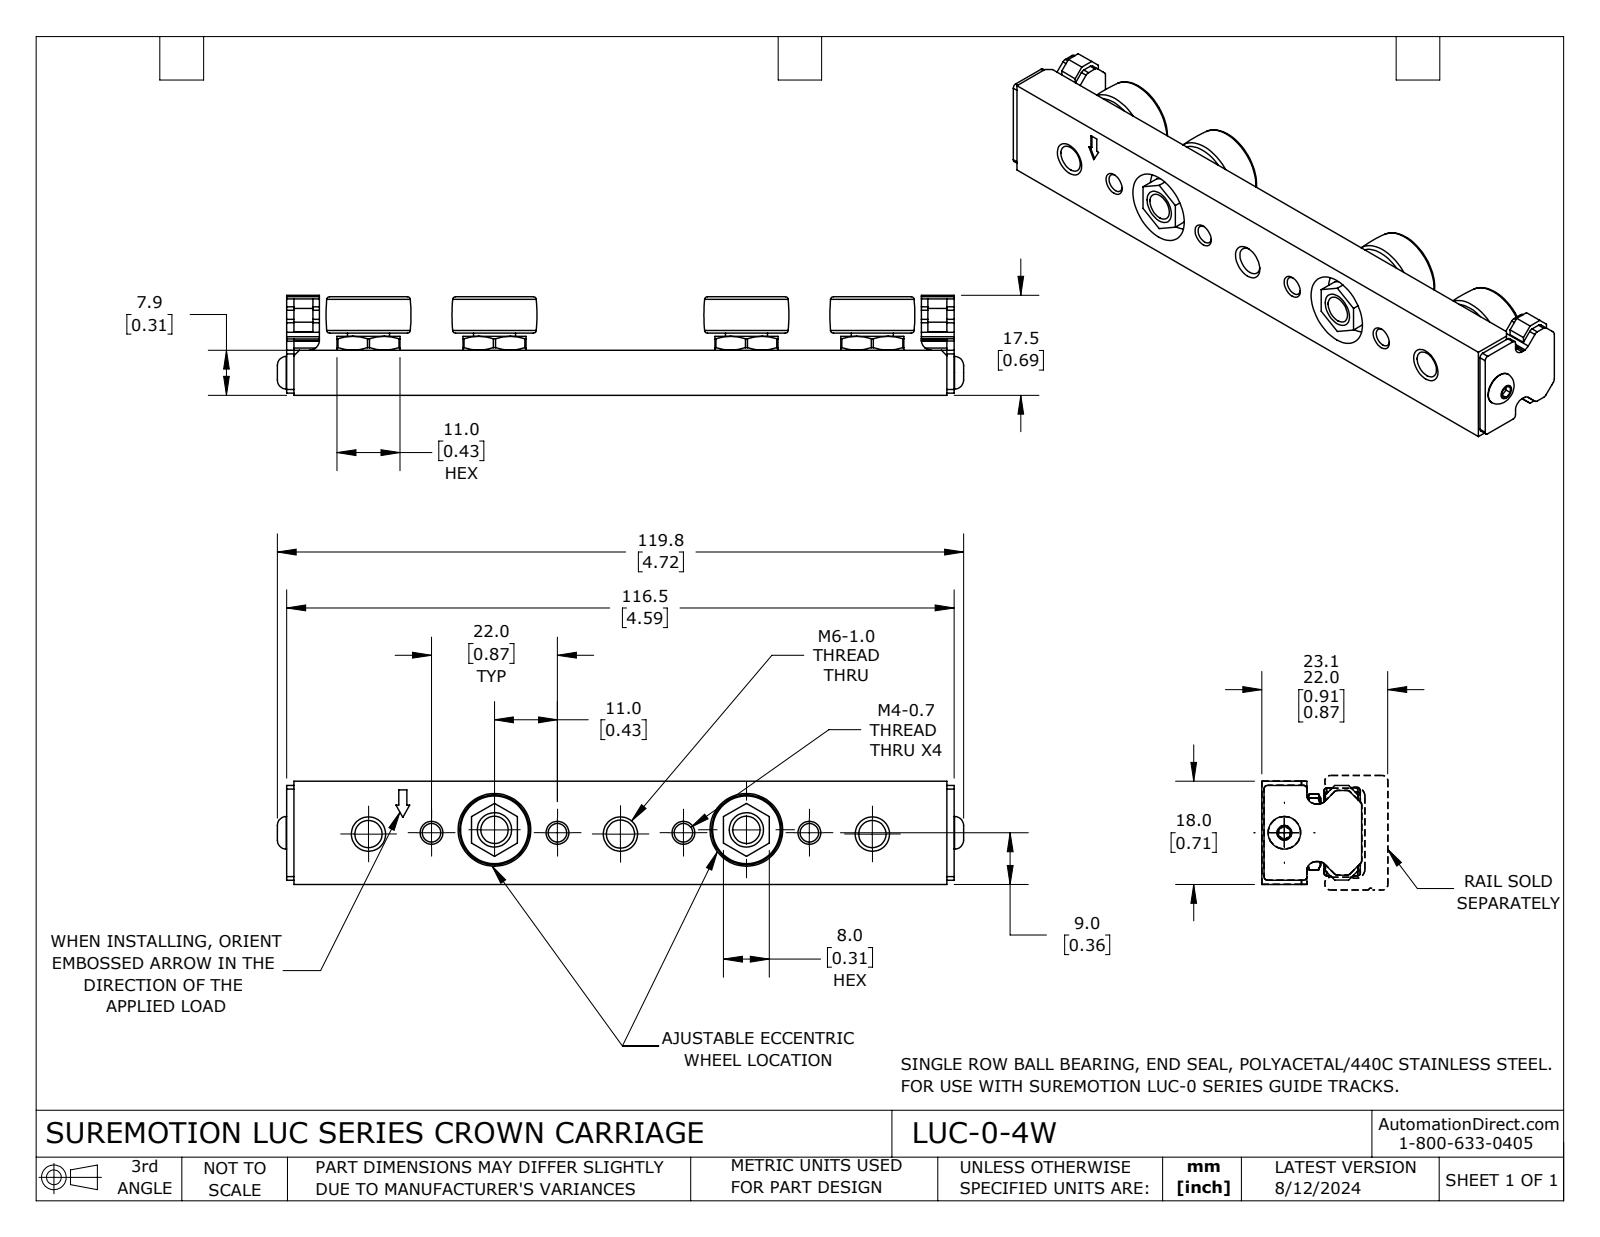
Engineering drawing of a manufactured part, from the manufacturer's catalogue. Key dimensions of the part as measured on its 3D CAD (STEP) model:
Part name (STEP PRODUCT): LUC-0-4W
STEP written by: SolidWorks 2023 (CONFIG_CONTROL_DESIGN)
Units: inches
Bodies: 9 solids, 572 faces (220 planar, 172 cylindrical, 180 other)
Overall size (bounding box): 4.718 × 0.709 × 0.687
Volume: 1.33 in³ · Surface area: 21.53 in²
Round holes (diameter × count): ⌀0.128 ×4, ⌀0.194 ×4, ⌀0.39 ×4, ⌀0.221 ×2, ⌀0.5 ×2, ⌀0.097 ×1, ⌀0.194 ×1
Round bosses / shafts (diameter × count): ⌀0.289 ×4, ⌀0.236 ×4, ⌀0.177 ×4, ⌀0.465 ×2, ⌀0.224 ×1, ⌀0.118 ×1
Partial cylindrical surfaces — rounded edges, fillets, slot ends (radius × count): R0.015 ×12, R0.033 ×6, R0.025 ×4, R0.063 ×4, R0.246 ×4, R0.07 ×2
Main face-to-face distances: 0.31, 0.709, 0.05, 4.538, 0.208, 0.042, 0.107, 0.203, 0.325, 0.432
Hole centre spacings: 0.433, 1.299, 1.732, 2.165, 0.866, 0.433, 0.866, 0.867
